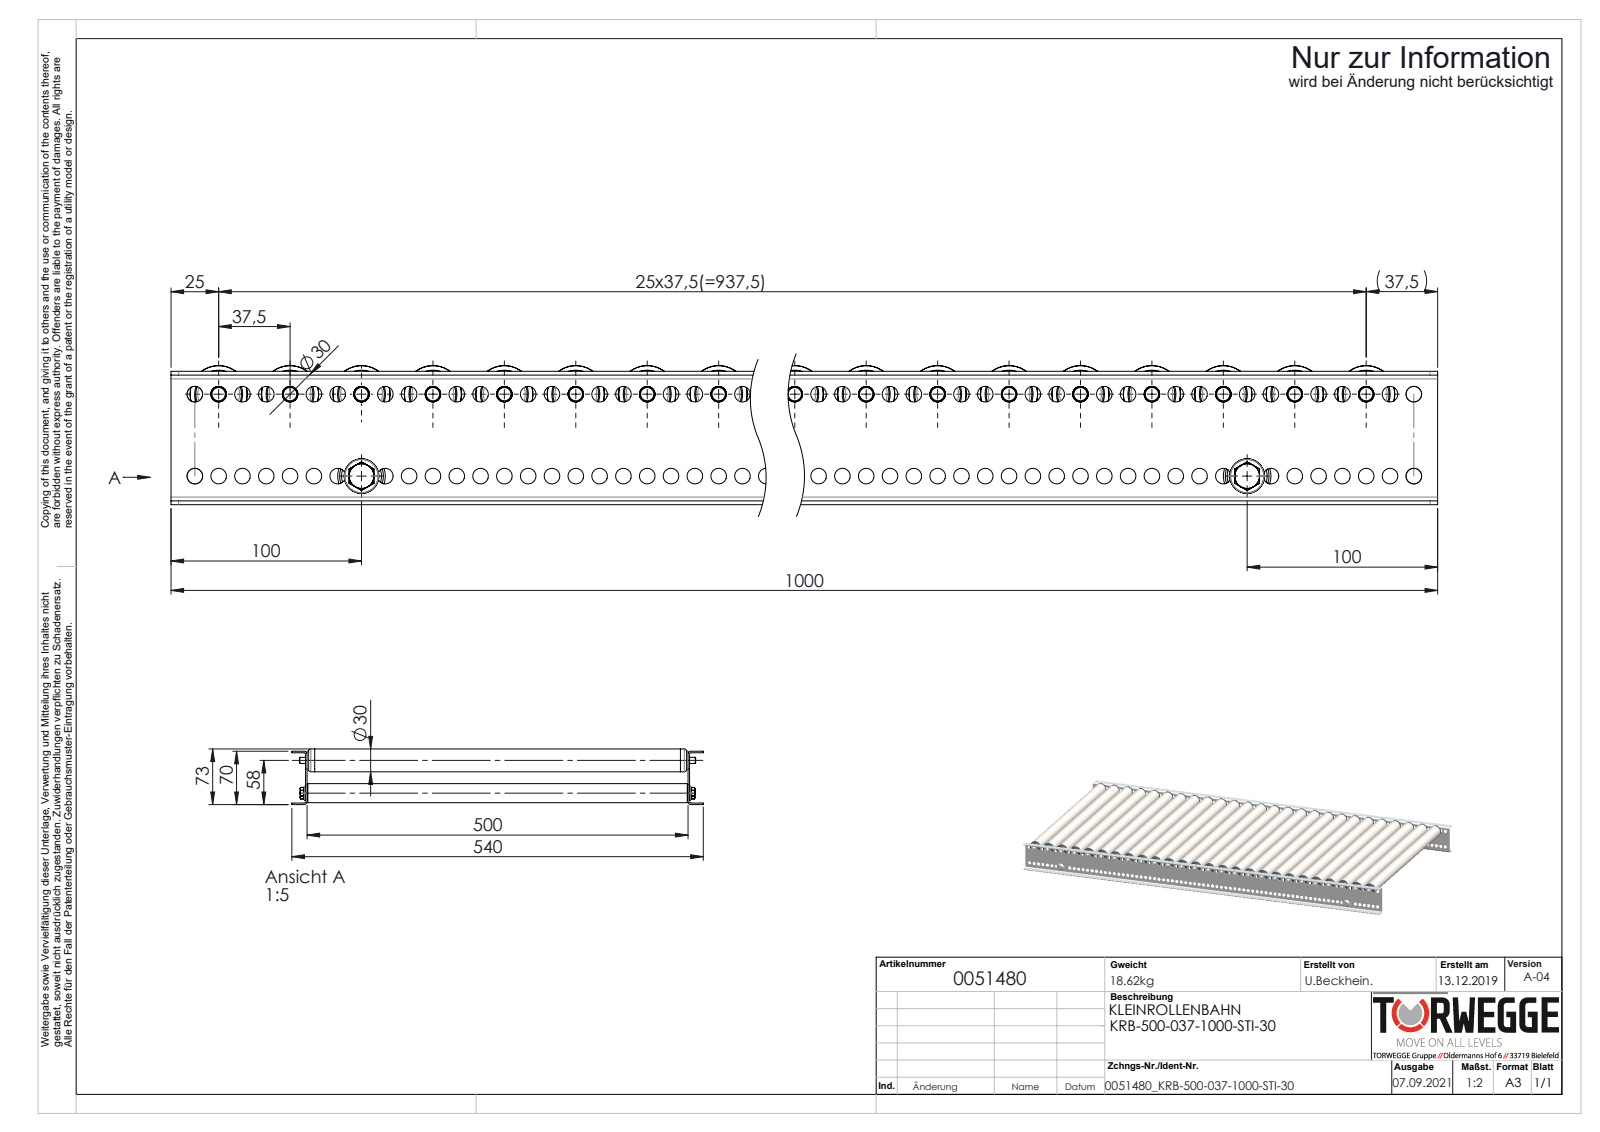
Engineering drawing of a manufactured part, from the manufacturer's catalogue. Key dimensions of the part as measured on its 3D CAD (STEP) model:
Part name (STEP PRODUCT): Profil_KRB-20x70x20x2_KFG_S100230_U-PROFIL-20-70-20-2-KRB-30-L=1000; 0024176_Passscheibe_DIN988_8x14x1; 0040250_DRUCK-FEDER-8mm; 0039768_Tragrollenrohr-Ø30x1,5STI_KFG_0039768_L=480 (+6 more)
STEP written by: SolidWorks 2020 (AUTOMOTIVE_DESIGN)
Units: millimetres
Bodies: 168 solids, 6996 faces (2200 planar, 2768 cylindrical, 2028 other)
Overall size (bounding box): 1000 × 540 × 73
Volume: 2 924 000 mm³ · Surface area: 3 512 000 mm²
Round holes (diameter × count): ⌀8.2 ×158, ⌀8 ×26, ⌀8.1 ×26, ⌀23.2 ×26, ⌀25.2 ×26, ⌀27 ×26, ⌀6.8 ×2, ⌀21 ×2
Round bosses / shafts (diameter × count): ⌀30 ×26, ⌀29.9 ×26, ⌀27.1 ×26, ⌀26.8 ×26, ⌀24 ×26, ⌀14 ×26, ⌀25 ×2, ⌀8 ×2
Partial cylindrical surfaces — rounded edges, fillets, slot ends (radius × count): R5.05 ×26, R4 ×8, R2 ×4
Main face-to-face distances: 2, 502, 500, 68, 504, 66, 70, 10, 490, 20
Hole centre spacings: 12.5, 25, 37.5, 50, 62.5, 75, 87.5, 100
